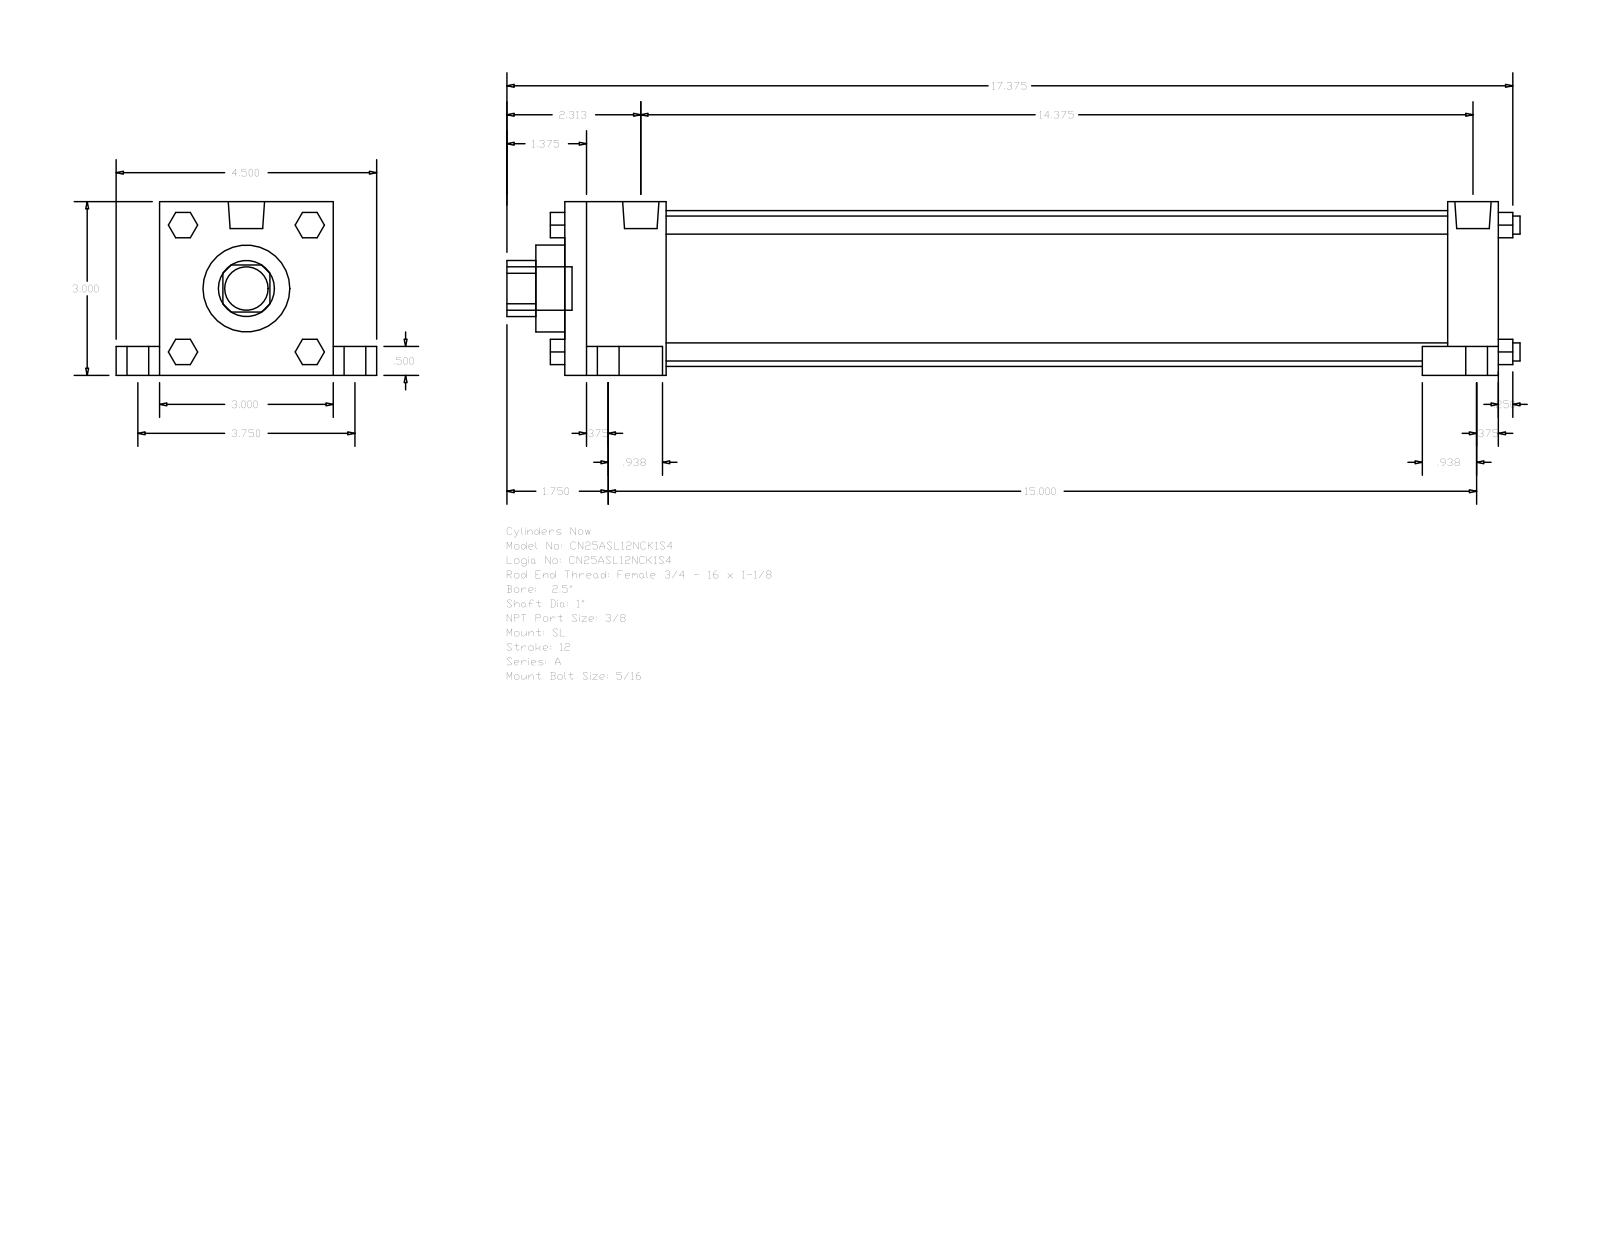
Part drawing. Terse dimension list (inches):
name: A_SL__0250_1
written by: GSSL Pune (CONFIG_CONTROL_DESIGN)
unit: in
bodies: 0 solids, 148 faces (112 planar, 36 cylindrical, 0 other)
size: 17.5 × 4.5 × 3
holes: 1× ⌀1, 1× ⌀1.5, 1× ⌀2.69
bosses: 4× ⌀0.625, 4× ⌀0.375, 4× ⌀0.313, 4× ⌀0.219, 2× ⌀0.627, 1× ⌀0.75
rounds: 1× R0.484
face distances: 3, 16.125, 0.5, 1.75, 14.375, 15.25, 13.5, 0.875, 0.75, 2.5
